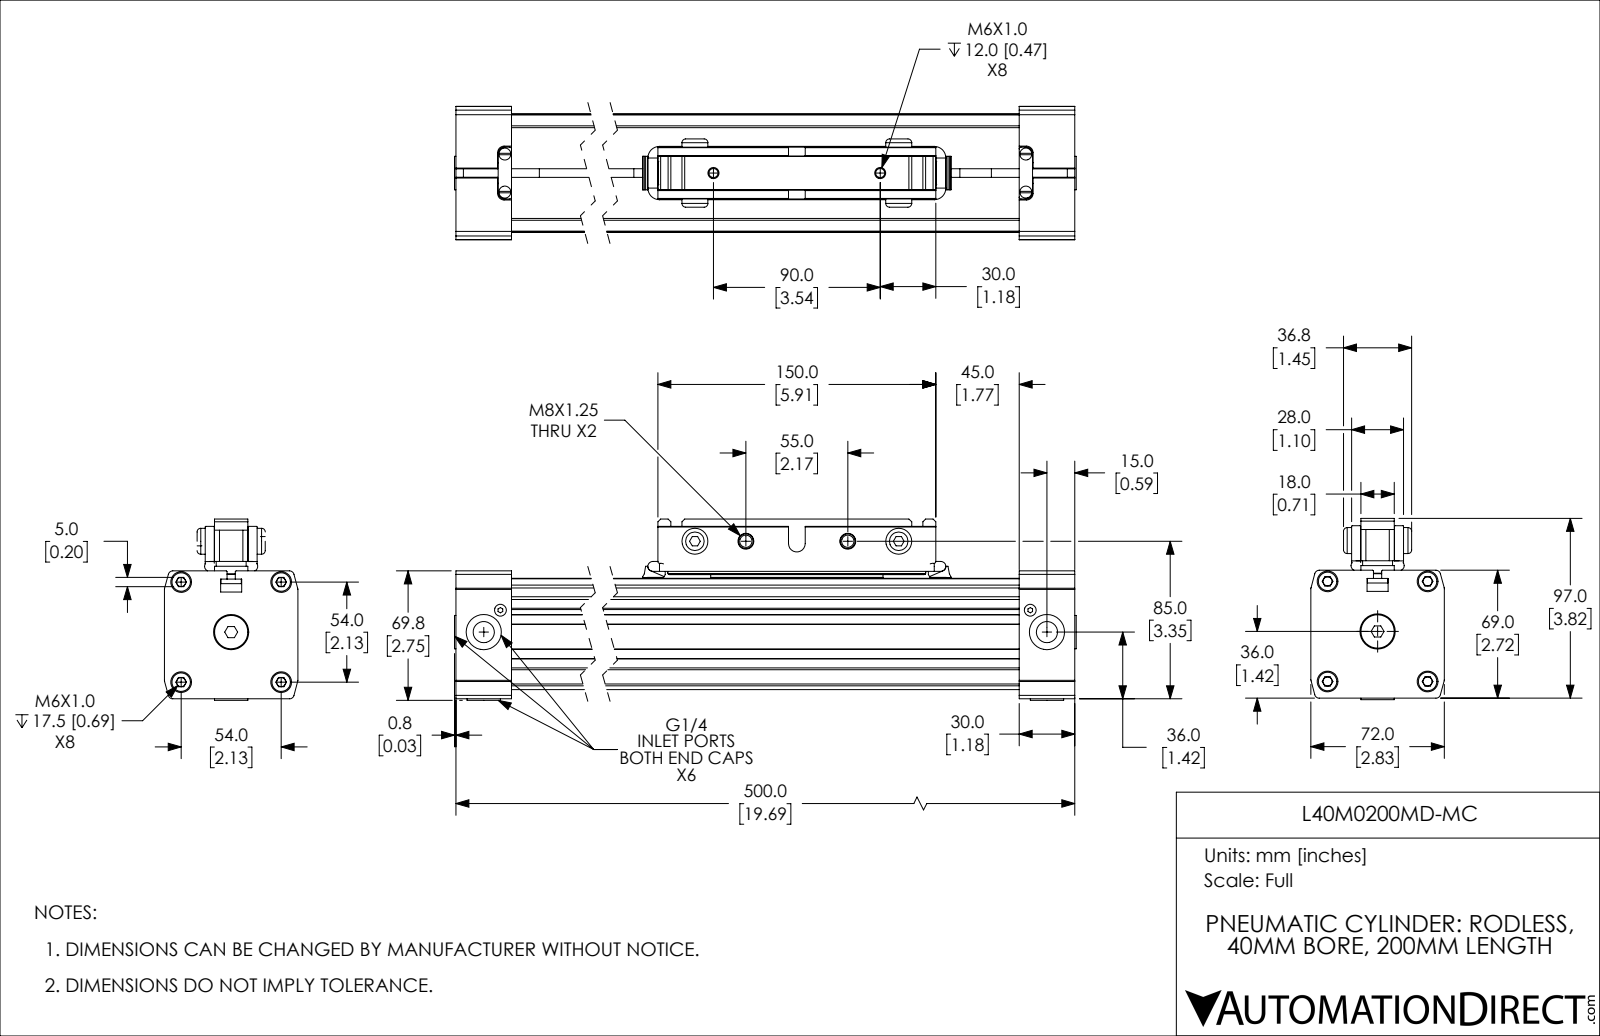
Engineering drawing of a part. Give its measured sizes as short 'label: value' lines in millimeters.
name: L40M0200MD-MC_BODY; L40M0200MD-MC_PISTON; L40M0200MD-MC
written by: SolidWorks 2019 (CONFIG_CONTROL_DESIGN)
unit: mm
bodies: 13 solids, 821 faces (451 planar, 278 cylindrical, 92 other)
size: 501.57 × 97.79 × 72
volume: 1 567 000 mm³; area: 330 159 mm²
holes: 6× ⌀4.92, 5× ⌀11.45, 5× ⌀19, 4× ⌀6.5, 4× ⌀6.65, 4× ⌀8.6, 4× ⌀11.2, 2× ⌀6.4, 1× ⌀40.2
bosses: 4× ⌀10, 4× ⌀5.33, 3× ⌀18, 3× ⌀11.1, 2× ⌀14, 2× ⌀13.16, 1× ⌀40, 1× ⌀13.16
rounds: 30× R1, 10× R2, 8× R0.3, 8× R2.5, 8× R3.5, 4× R4, 2× R0.15, 2× R0.2
face distances: 60, 5.1, 30, 17.8, 63.6, 45, 58.5, 470, 5, 22.68
hole spacings: 15.33, 38.18, 54, 458.71, 14.84, 20.5, 27.5, 36.26
